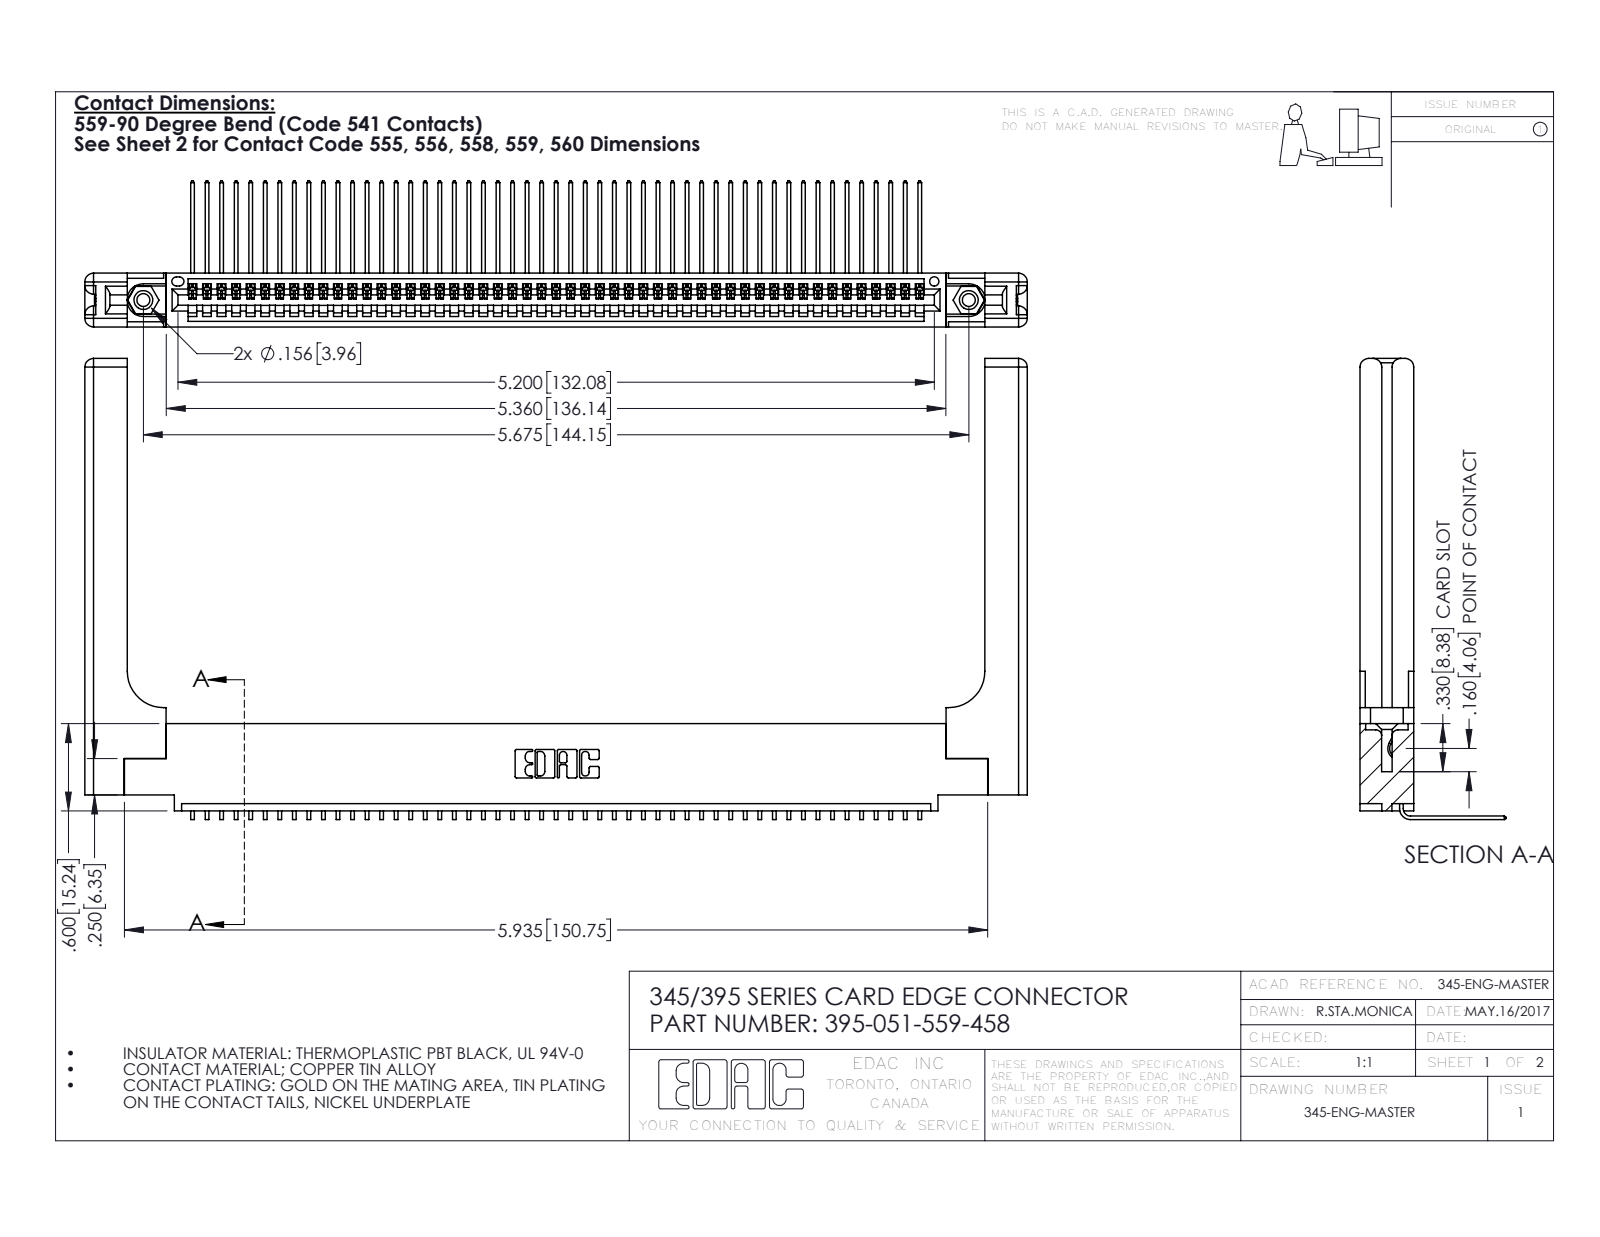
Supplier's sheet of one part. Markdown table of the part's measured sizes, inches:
| quantity | value |
| --- | --- |
| part name | 345 Part_0.110 Offset - 0.156 Dia-TH; 345-220-058_345-220-058; 345-292-001_558 559 Tail - 1; 395-051-559-458 (+1 more) |
| STEP written by | SolidWorks 2016 (CONFIG_CONTROL_DESIGN) |
| units | inches |
| bodies | 56 solids, 3446 faces (2374 planar, 1012 cylindrical, 60 other) |
| overall size | 6.479 × 3.169 × 1.005 |
| volume | 1.483 in³ |
| surface area | 42.63 in² |
| round holes (diameter × count) | 0.089 × 2, 0.125 × 2, 0.156 × 2, 0.064 × 1 |
| round bosses / shafts (diameter × count) | 0.155 × 2 |
| partial cylindrical surfaces (radius × count) | 0.006 × 102, 0.01 × 22, 0.06 × 16, 0.007 × 6, 0.031 × 6, 0.026 × 3, 0.03 × 2, 0.031 × 2 |
| main face-to-face distances | 0.37, 0.072, 0.298, 0.098, 0.272, 0.025, 0.2, 0.225, 0.148, 0.15 |
| hole center spacings | 0.27, 5.439, 5.675 |
